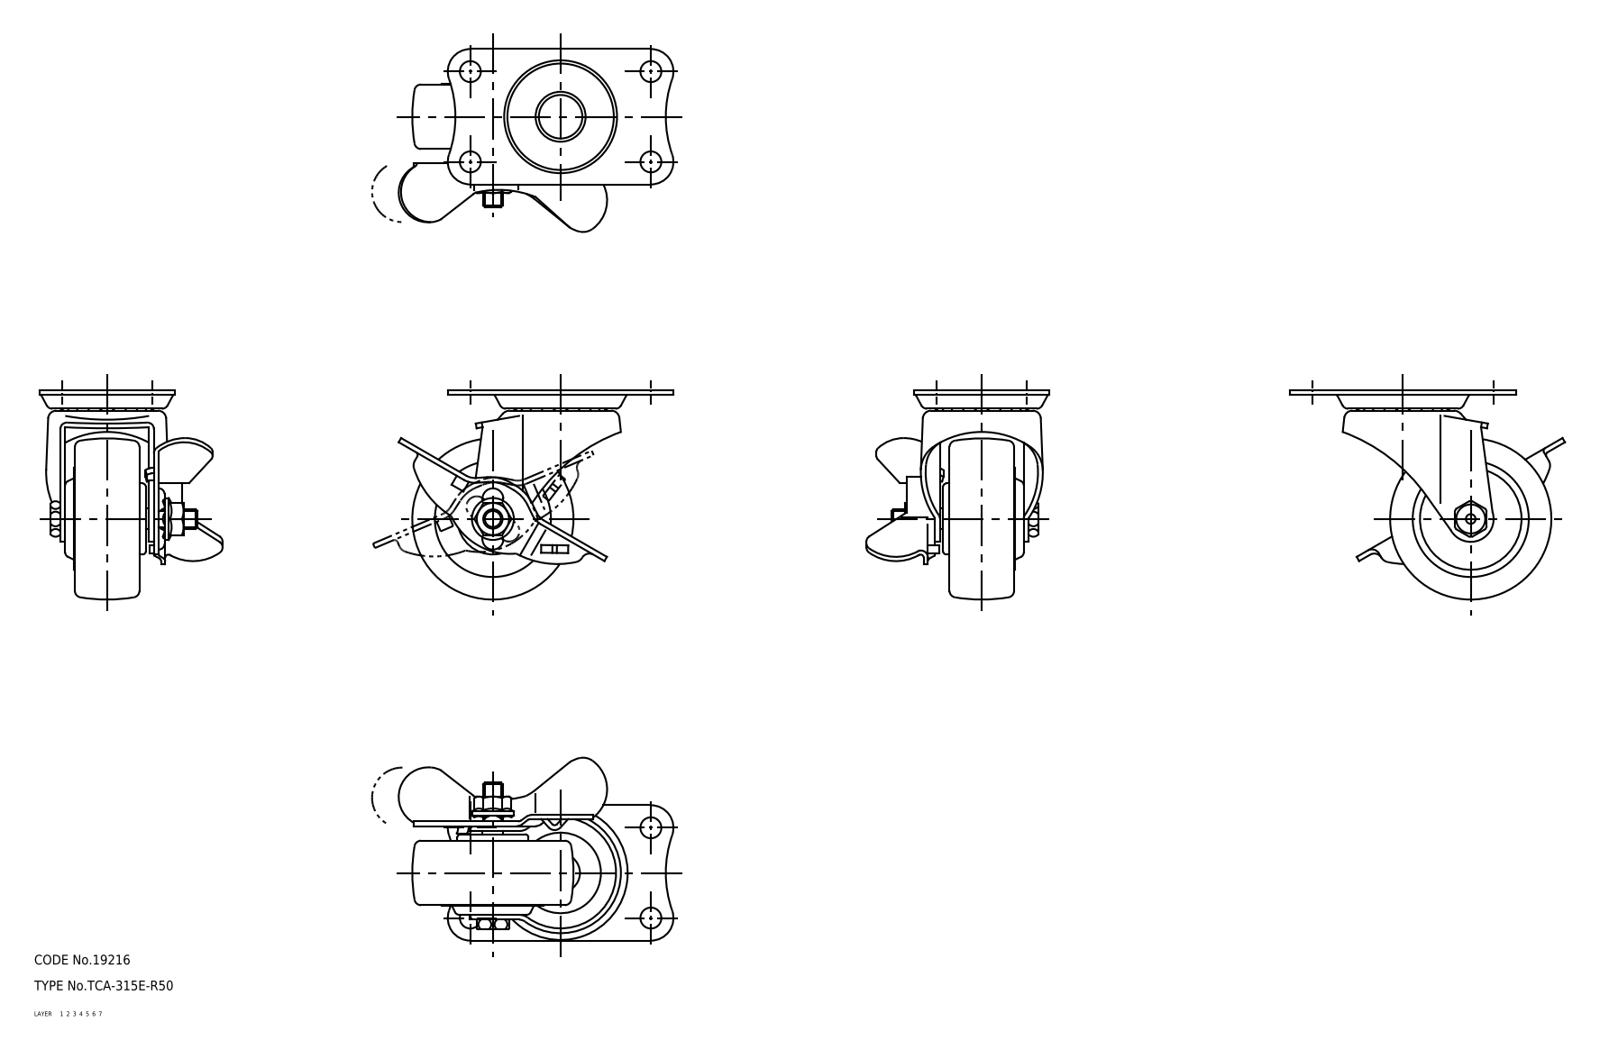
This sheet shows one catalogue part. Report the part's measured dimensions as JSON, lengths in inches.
{"part_name": "wheel; mounting plate; main shaft; lever (+2 more)", "step_written_by": "CADfix (AUTOMOTIVE_DESIGN)", "units": "inches", "bodies": {"solids": 12, "faces": 414, "planar": 0, "cylindrical": 0, "other": 414}, "overall_size": [3.355, 2.559, 2.234], "volume_in3": 3.397, "surface_area_in2": 44.21}
